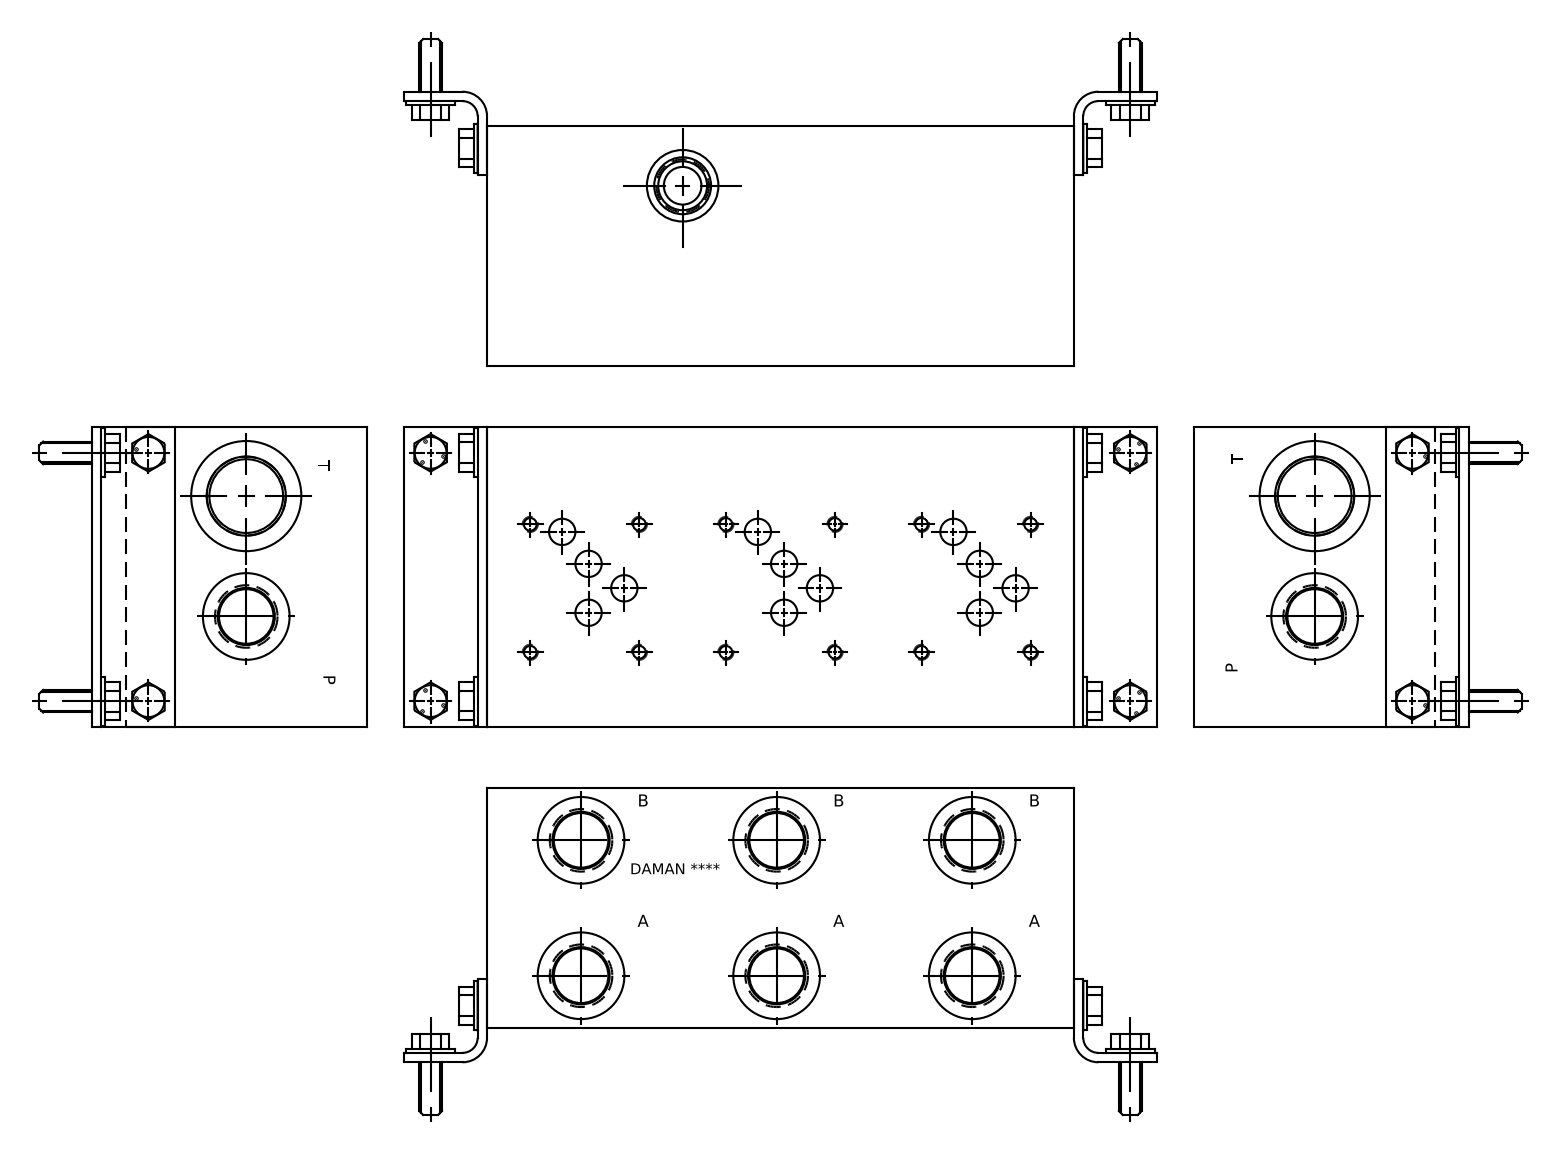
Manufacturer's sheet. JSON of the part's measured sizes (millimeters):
{"part_name": "Part_AD05HP033B~C_3D", "step_written_by": "Autodesk Inventor 2019 (AUTOMOTIVE_DESIGN)", "units": "millimeters", "bodies": {"solids": 1, "faces": 728, "planar": 398, "cylindrical": 90, "other": 240}, "overall_size": [247.65, 127, 101.6], "volume_mm3": 2980000, "surface_area_mm2": 177161, "round_holes": [[5, 12], [5.99, 12], [11.13, 10], [23.01, 7], [24.41, 7], [26.54, 7], [37.11, 7], [8.51, 2], [10.01, 2], [11.11, 2], [14.29, 1], [15.9, 1]], "face_to_face_distances": [101.6, 127, 247.65, 0.79, 126.21, 246.86, 246.07, 17.88, 17.09, 109.12], "hole_center_spacings": [82.55, 98.63, 165.1, 46.05, 70.95, 53.98, 18.27, 29.74]}
